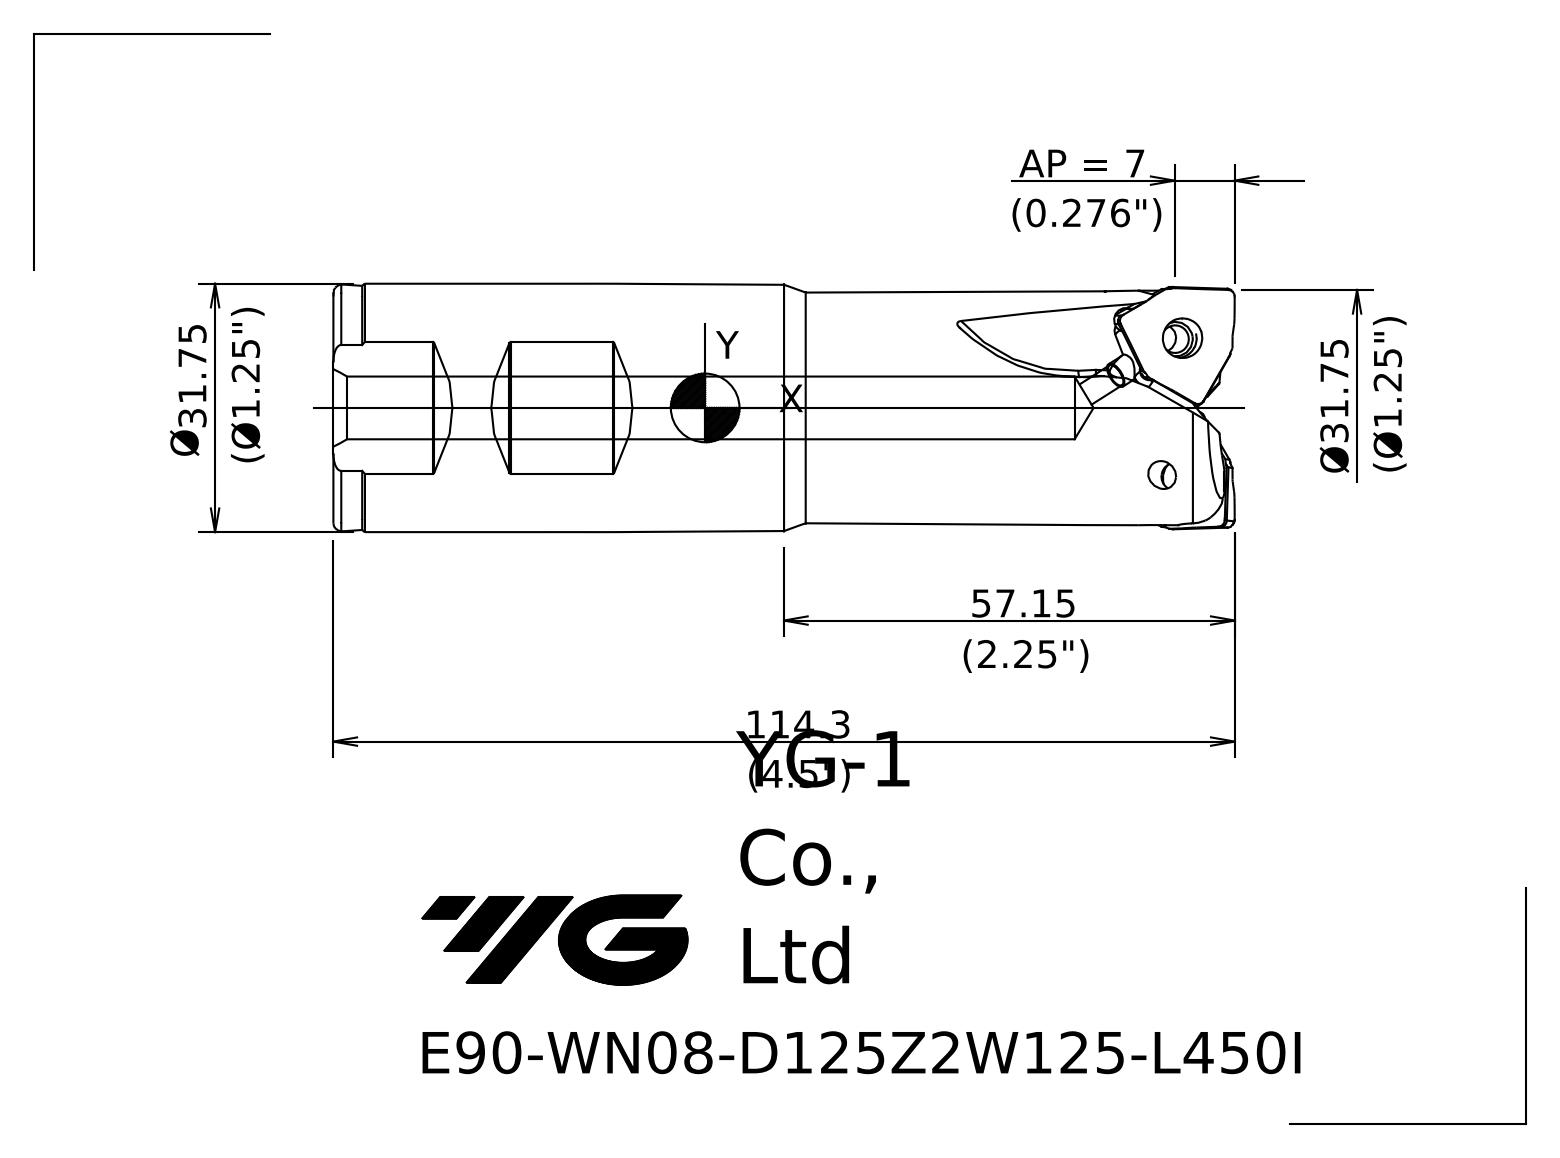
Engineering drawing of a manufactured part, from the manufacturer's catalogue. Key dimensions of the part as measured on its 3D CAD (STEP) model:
Part name (STEP PRODUCT): 10224990B0573z61
STEP written by: SIEMENS PLM Software NX 10.0 (AP203_CONFIGURATION_CONTROLLED_3D_DESIGN_OF_MECHANICAL_PARTS_AND_ASSEMBLIES_MIM_LF)
Units: millimetres
Bodies: 1 solid, 63 faces (8 planar, 7 cylindrical, 48 other)
Overall size (bounding box): 114.3 × 31.75 × 31.75
Volume: 77 918 mm³ · Surface area: 17 566 mm²
Round holes (diameter × count): ⌀8 ×1
Round bosses / shafts (diameter × count): ⌀31.75 ×1, ⌀31.35 ×1, ⌀29.75 ×1
Partial cylindrical surfaces — rounded edges, fillets, slot ends (radius × count): R0.3 ×3
Main face-to-face distances: 113, 16.14, 3.2, 109.8
